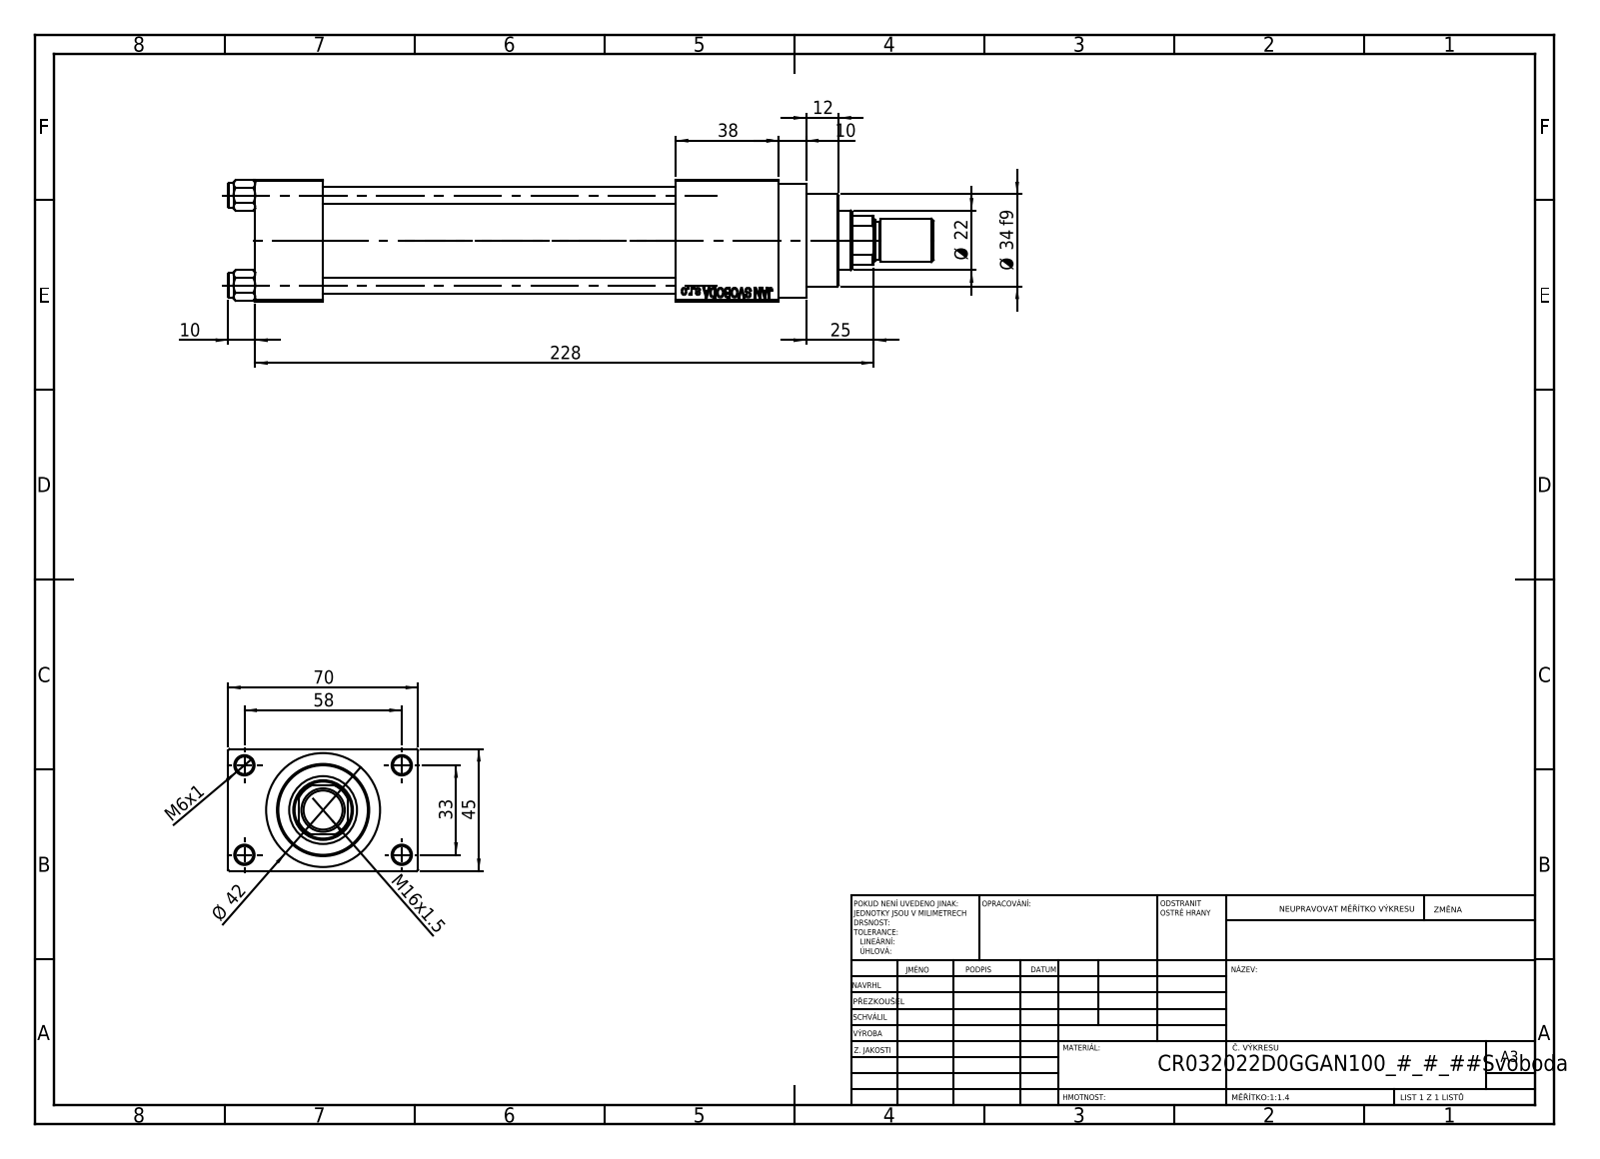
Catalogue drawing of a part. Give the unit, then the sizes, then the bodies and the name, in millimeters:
Units: millimetres
Overall size (bounding box): 260 × 70 × 45
Round holes (diameter × count): ⌀6 ×4, ⌀6.5 ×4, ⌀7 ×2, ⌀13.16 ×2, ⌀20 ×2, ⌀10.5 ×1, ⌀22 ×1, ⌀24 ×1, ⌀25 ×1, ⌀32 ×1, ⌀33 ×1
Round bosses / shafts (diameter × count): ⌀9 ×4, ⌀42 ×1, ⌀38 ×1, ⌀34 ×1, ⌀16 ×1, ⌀14 ×1
Partial cylindrical surfaces — rounded edges, fillets, slot ends (radius × count): R10.5 ×1
Main face-to-face distances: 45, 25, 12.5, 57.5, 130, 155, 168, 70, 38, 193
Hole centre spacings: 12.4, 23.48, 33.2, 33.37, 35.35, 45.6, 56.35, 33
Volume: 314 774 mm³ · Surface area: 110 151 mm²
Bodies: 12 solids, 1117 faces (500 planar, 93 cylindrical, 524 other)
Part name (STEP PRODUCT): V215_VC_A; NUT_M5_D; V215CR_D_Body; V215CR_VCP_D (+2 more)
STEP written by: SolidWorks 2019 (CONFIG_CONTROL_DESIGN)
